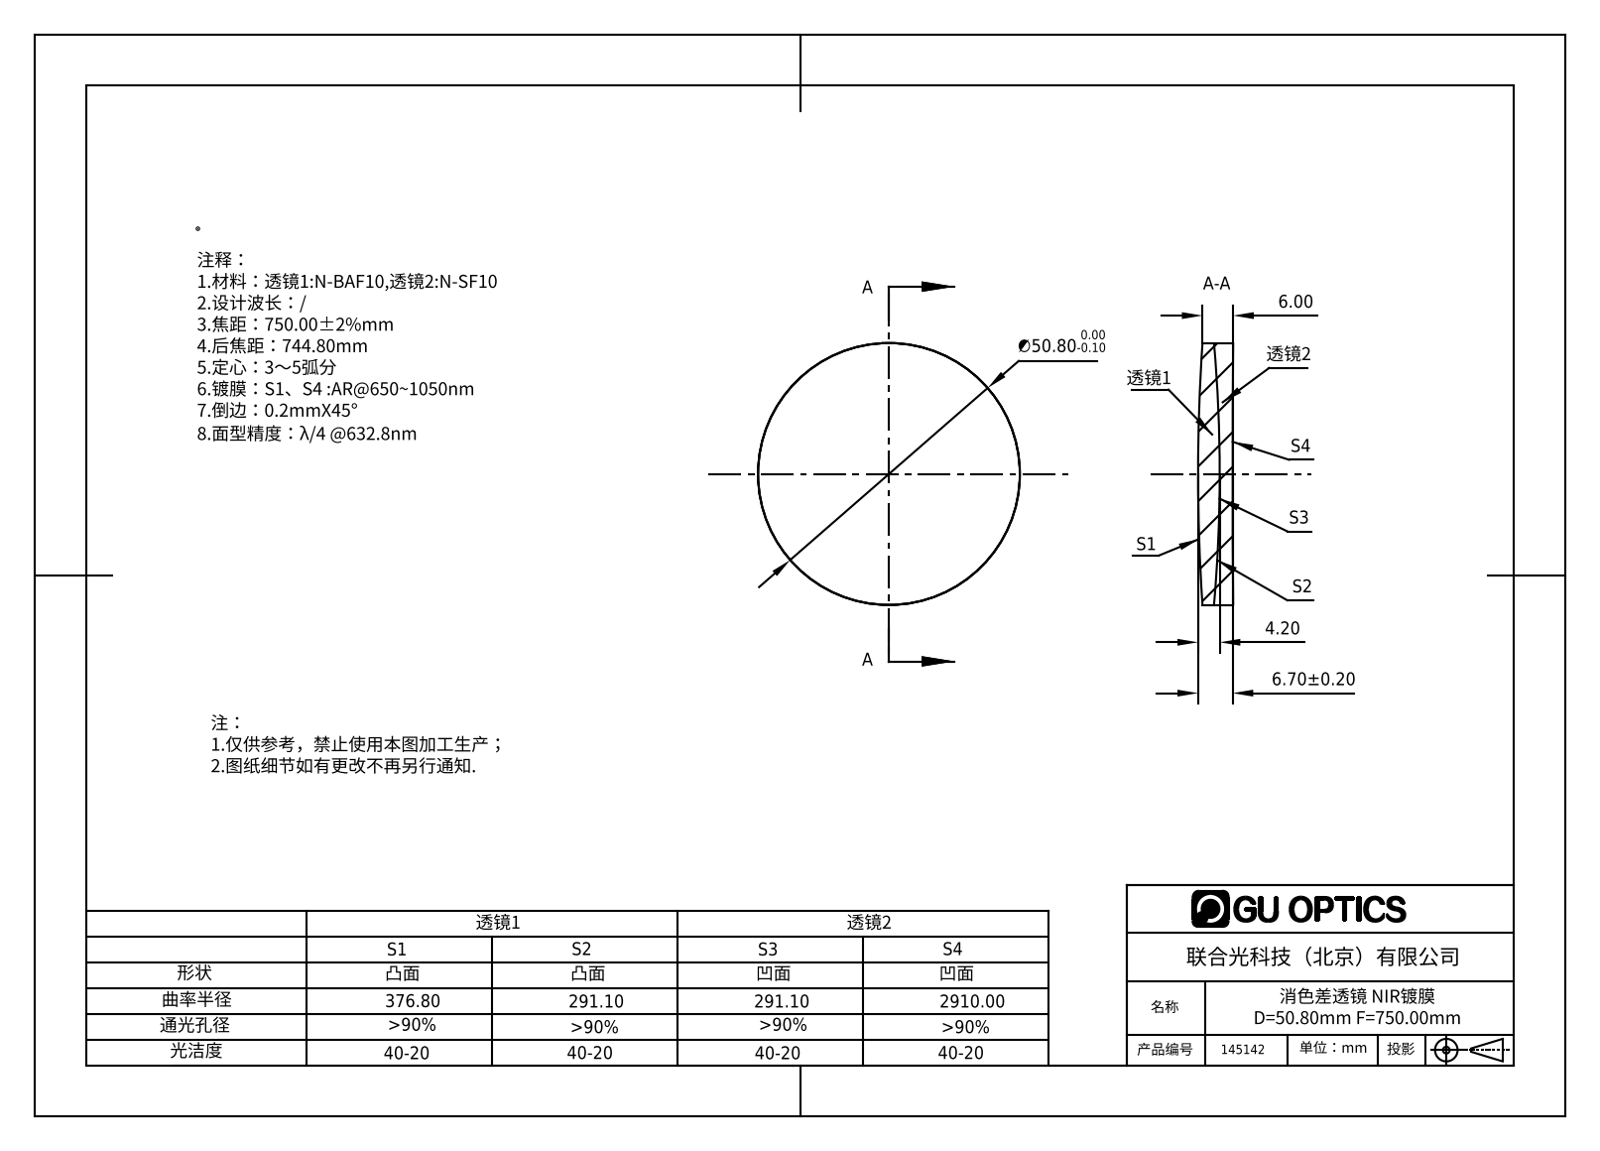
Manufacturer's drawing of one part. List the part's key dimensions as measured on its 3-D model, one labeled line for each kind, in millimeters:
Part name (STEP PRODUCT): 145142
STEP written by: SolidWorks 2016 (AUTOMOTIVE_DESIGN)
Units: millimetres
Bodies: 2 solids, 12 faces (0 planar, 4 cylindrical, 8 other)
Overall size (bounding box): 50.8 × 50.8 × 6.81
Volume: 12 824 mm³ · Surface area: 9 068 mm²
Round bosses / shafts (diameter × count): ⌀50.8 ×1
